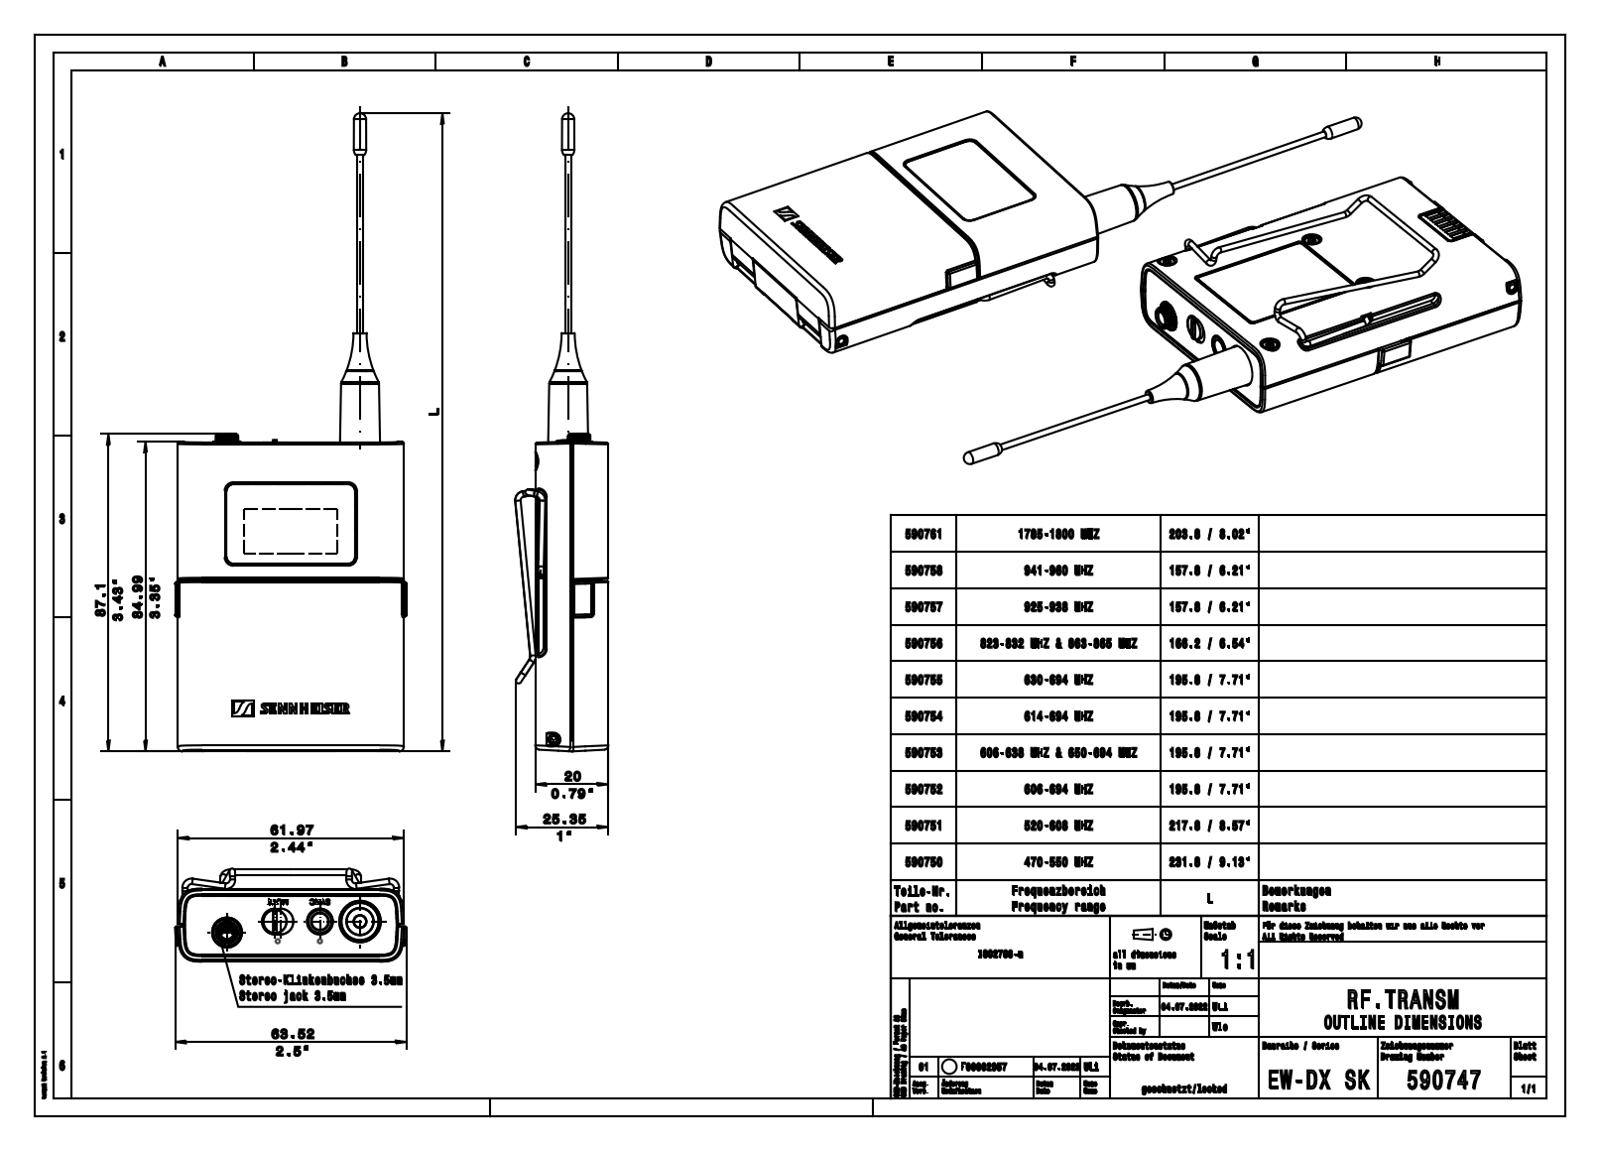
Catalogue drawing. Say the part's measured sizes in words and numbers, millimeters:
The part is named "590700-devoass-02; 590706-05; 590708-03; Locking (+8 more)". Its 3-D file was written by "Windows (AUTOMOTIVE_DESIGN)". It is 115 solids with 10380 faces: 0 planar, 0 cylindrical and 10380 other. Overall it measures 206.46 by 63.52 by 42.59 millimeters. Its volume is 50 587 cubic millimeters and its surface area 94 580 square millimeters.
